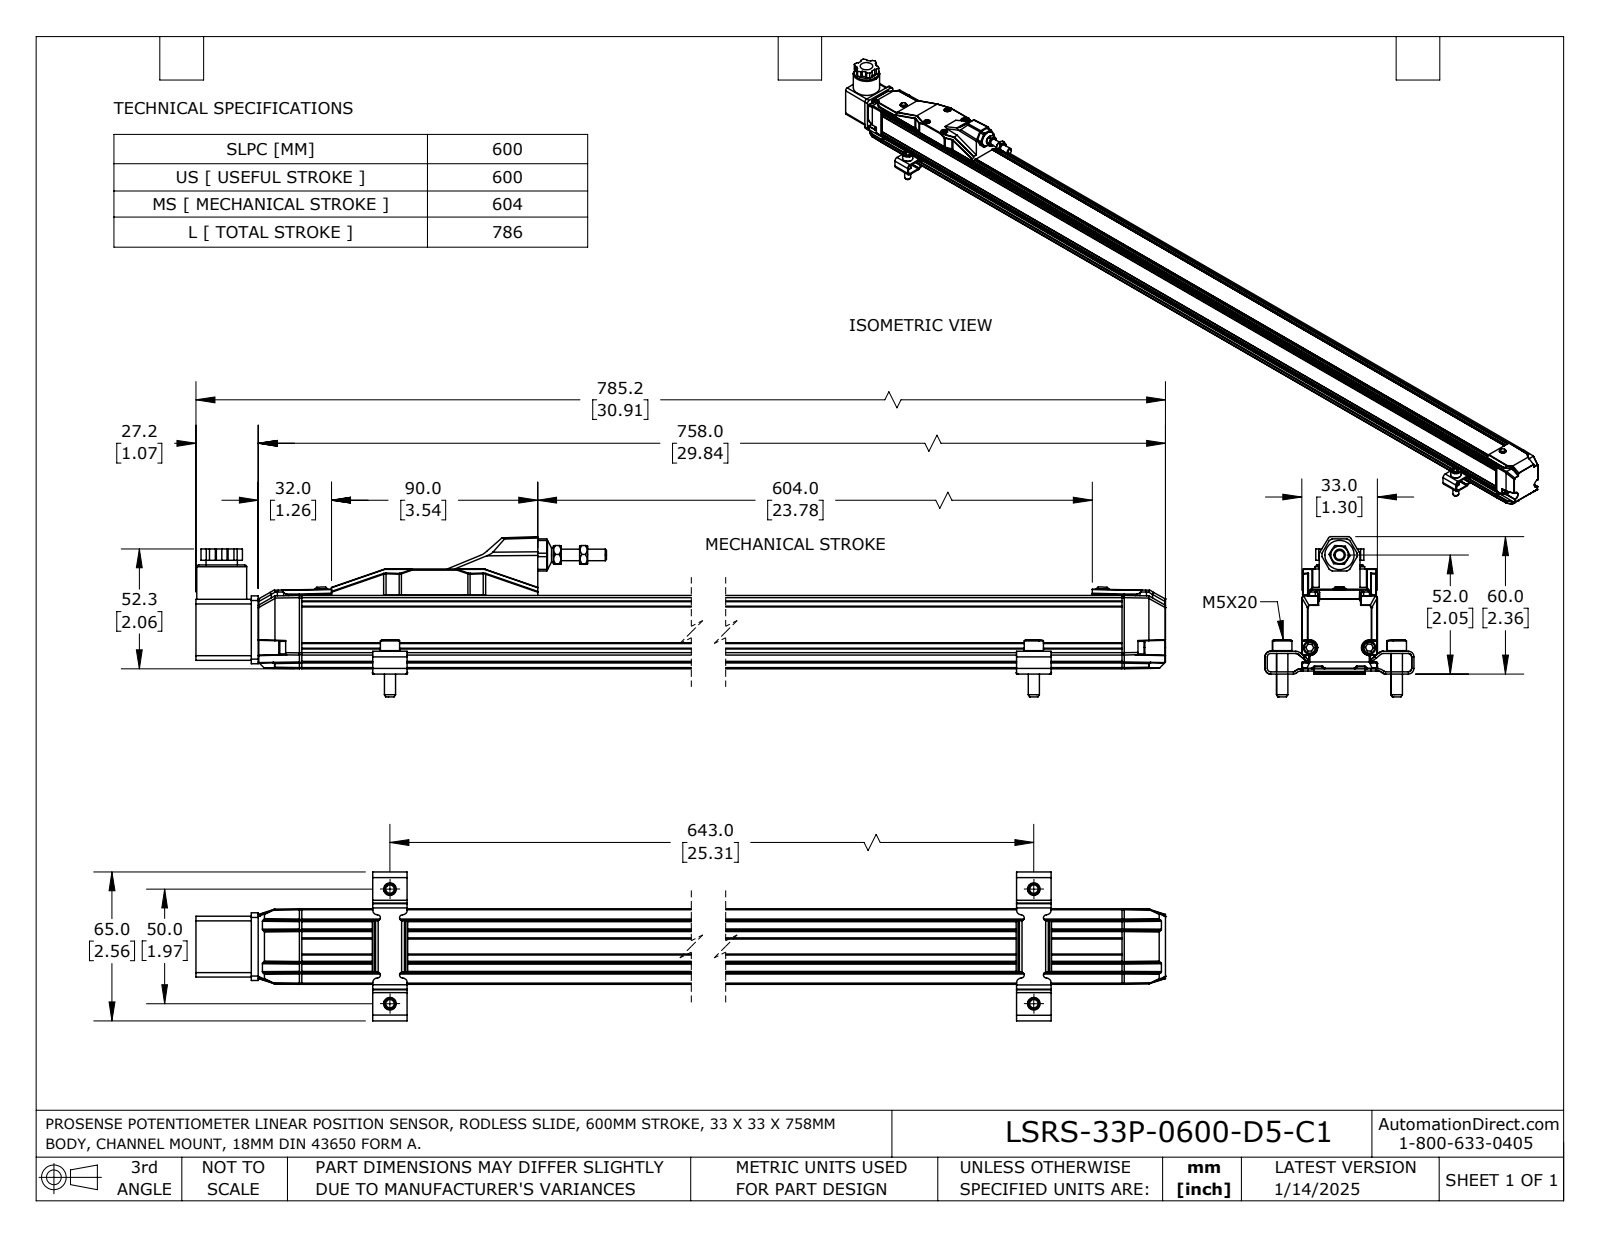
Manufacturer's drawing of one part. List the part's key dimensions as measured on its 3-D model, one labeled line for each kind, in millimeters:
Part name (STEP PRODUCT): LSRS-33P-0600-D5-C1
STEP written by: SolidWorks 2023 (AUTOMOTIVE_DESIGN)
Units: millimetres
Bodies: 28 solids, 1319 faces (814 planar, 373 cylindrical, 132 other)
Overall size (bounding box): 785.2 × 70 × 65
Volume: 752 200 mm³ · Surface area: 189 200 mm²
Round holes (diameter × count): ⌀2.7 ×6, ⌀4.7 ×4, ⌀5.5 ×4, ⌀3.3 ×2, ⌀2.8 ×1, ⌀4 ×1, ⌀5 ×1, ⌀5.3 ×1, ⌀5.9 ×1, ⌀6 ×1, ⌀7 ×1, ⌀10 ×1
Round bosses / shafts (diameter × count): ⌀8.4 ×4, ⌀4.9 ×4, ⌀4.6 ×4, ⌀2.9 ×4, ⌀5.6 ×2, ⌀5.5 ×2, ⌀3 ×2, ⌀2.5 ×2
Partial cylindrical surfaces — rounded edges, fillets, slot ends (radius × count): R0.5 ×82, R0.2 ×62, R2 ×44, R3 ×26, R1 ×10, R1.3 ×8, R1.5 ×8, R4 ×8
Main face-to-face distances: 33, 3, 31.6, 29.6, 6, 25.6, 0.9, 0.4, 32.6, 11.3
Hole centre spacings: 15.2, 20, 23.7, 31, 32.7, 42.5, 50, 613.6
